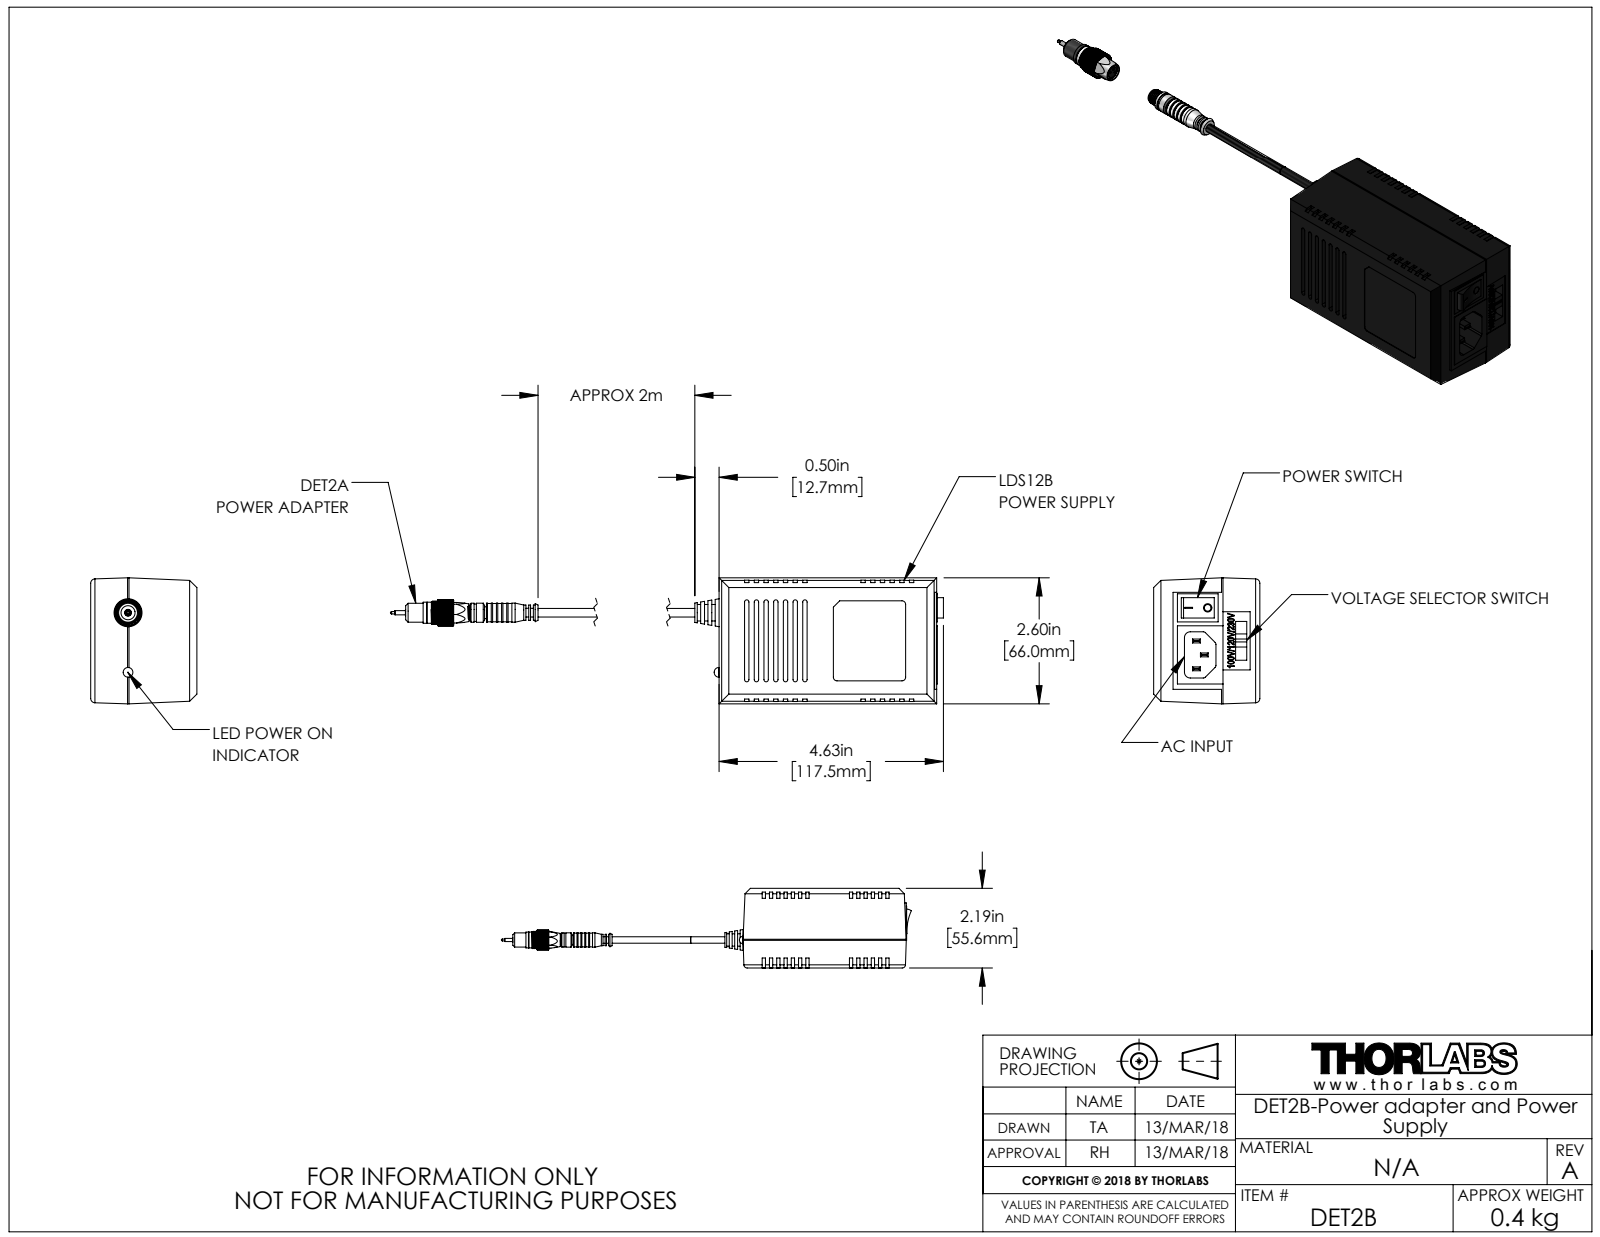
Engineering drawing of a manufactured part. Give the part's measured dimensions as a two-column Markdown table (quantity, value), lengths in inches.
| quantity | value |
| --- | --- |
| part name | TTN154011-E0W |
| STEP written by | SolidWorks 2016 (AUTOMOTIVE_DESIGN) |
| units | inches |
| bodies | 9 solids, 1089 faces (750 planar, 204 cylindrical, 135 other) |
| overall size | 11.272 × 2.598 × 2.19 |
| volume | 24.57 in³ |
| surface area | 72.44 in² |
| round holes (diameter × count) | 0.039 × 3, 0.043 × 3, 0.065 × 3, 0.067 × 1, 0.1 × 1, 0.14 × 1, 0.213 × 1, 0.228 × 1, 0.236 × 1, 0.248 × 1, 0.256 × 1, 0.268 × 1 |
| round bosses / shafts (diameter × count) | 0.063 × 3, 0.055 × 3, 0.039 × 3, 0.394 × 2, 0.315 × 2, 0.472 × 1, 0.435 × 1, 0.435 × 1 |
| partial cylindrical surfaces (radius × count) | 0.045 × 14, 0.06 × 4, 0.09 × 4, 0.075 × 3, 0.12 × 2, 0.005 × 1, 0.01 × 1, 0.25 × 1 |
| main face-to-face distances | 2.19, 0.2, 0.4, 2.18, 0.6, 0.09, 0.8, 0.11, 0.29, 0.49 |
| hole center spacings | 0.069, 0.098, 0.138 |
